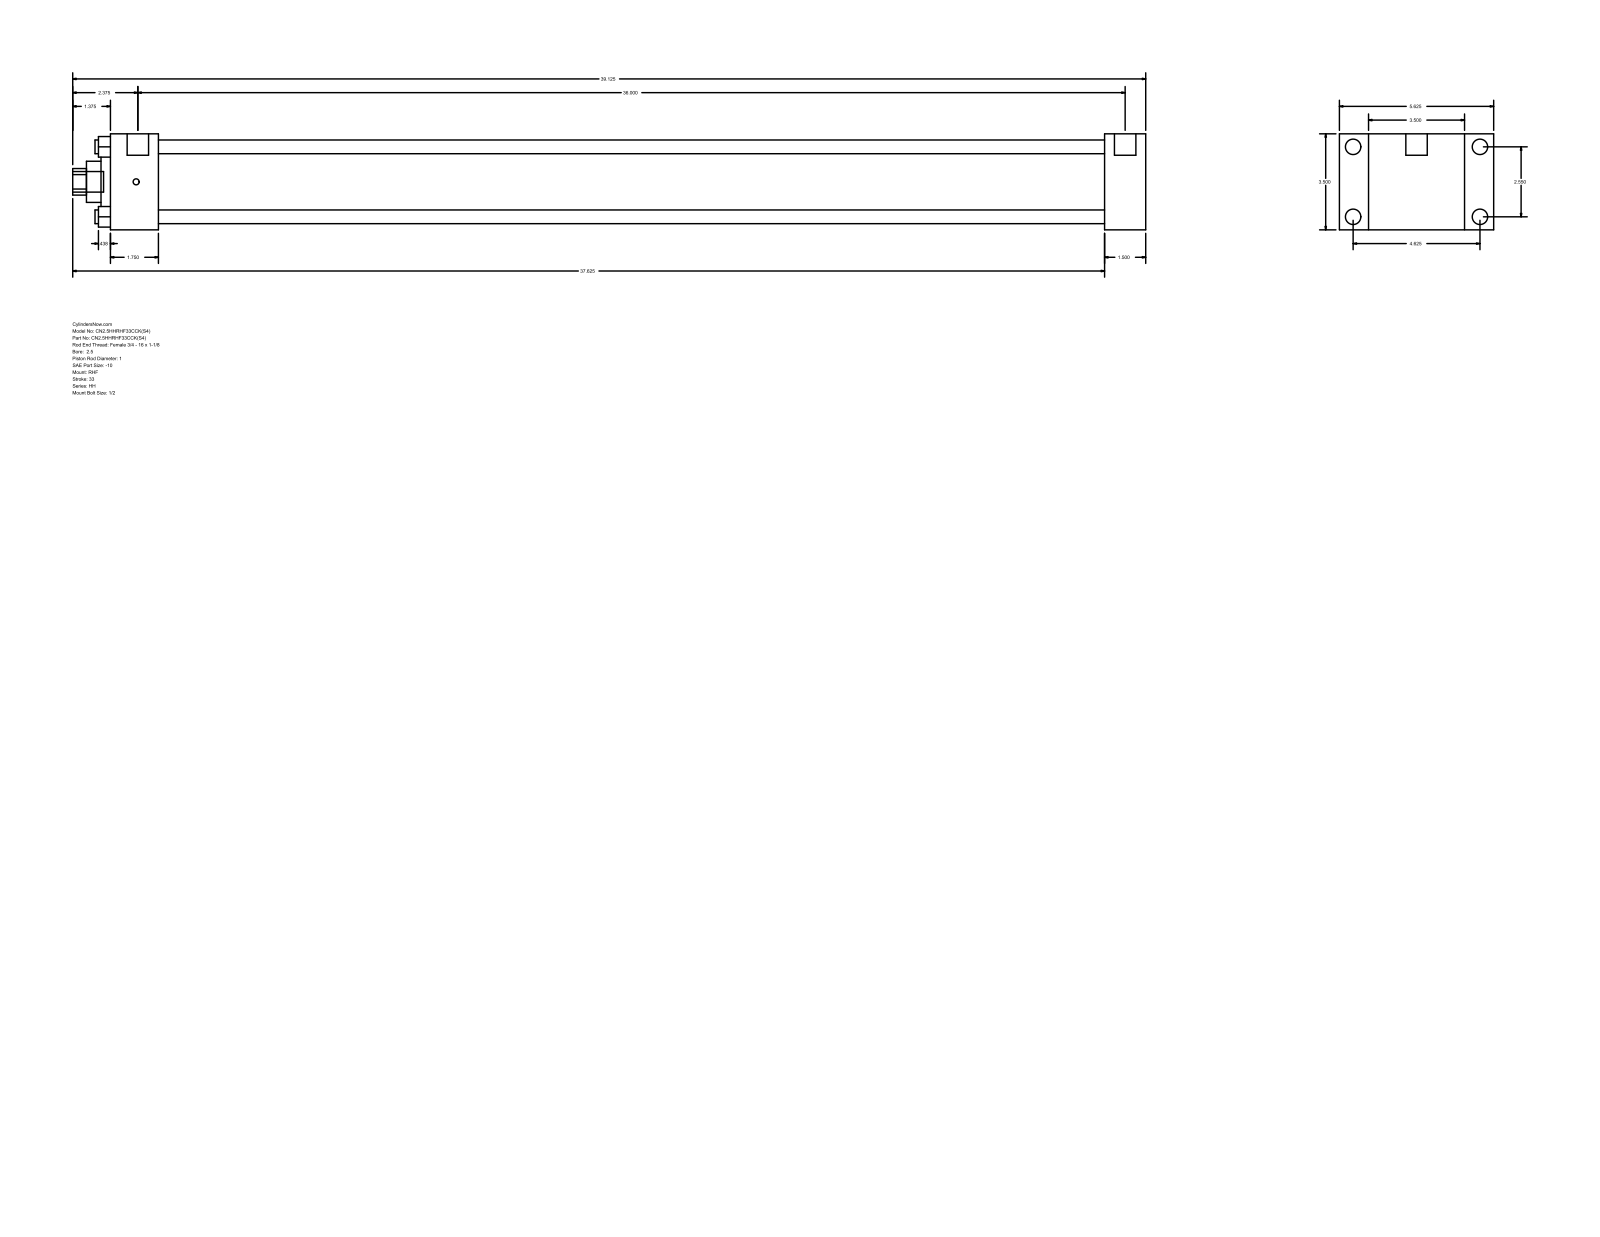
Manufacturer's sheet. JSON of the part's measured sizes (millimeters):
{"part_name": "HH_RHF__0250_1", "step_written_by": "GSSL Pune (CONFIG_CONTROL_DESIGN)", "units": "millimeters", "bodies": {"solids": 0, "faces": 90, "planar": 61, "cylindrical": 29, "other": 0}, "overall_size": [993.77, 142.88, 88.9], "round_holes": [[12.7, 4], [25.4, 1], [38.1, 1], [60.33, 1], [73.03, 1]], "round_bosses_or_shafts": [[14.3, 4], [5.56, 4], [19.84, 2], [19.05, 1]], "partial_cylinders_radius": [[12.29, 1]], "face_to_face_distances": [88.9, 38.1, 26.99, 115.89, 920.75, 958.85, 142.88, 44.46, 876.29, 914.39], "hole_center_spacings": [45.79, 64.76, 91.58]}
